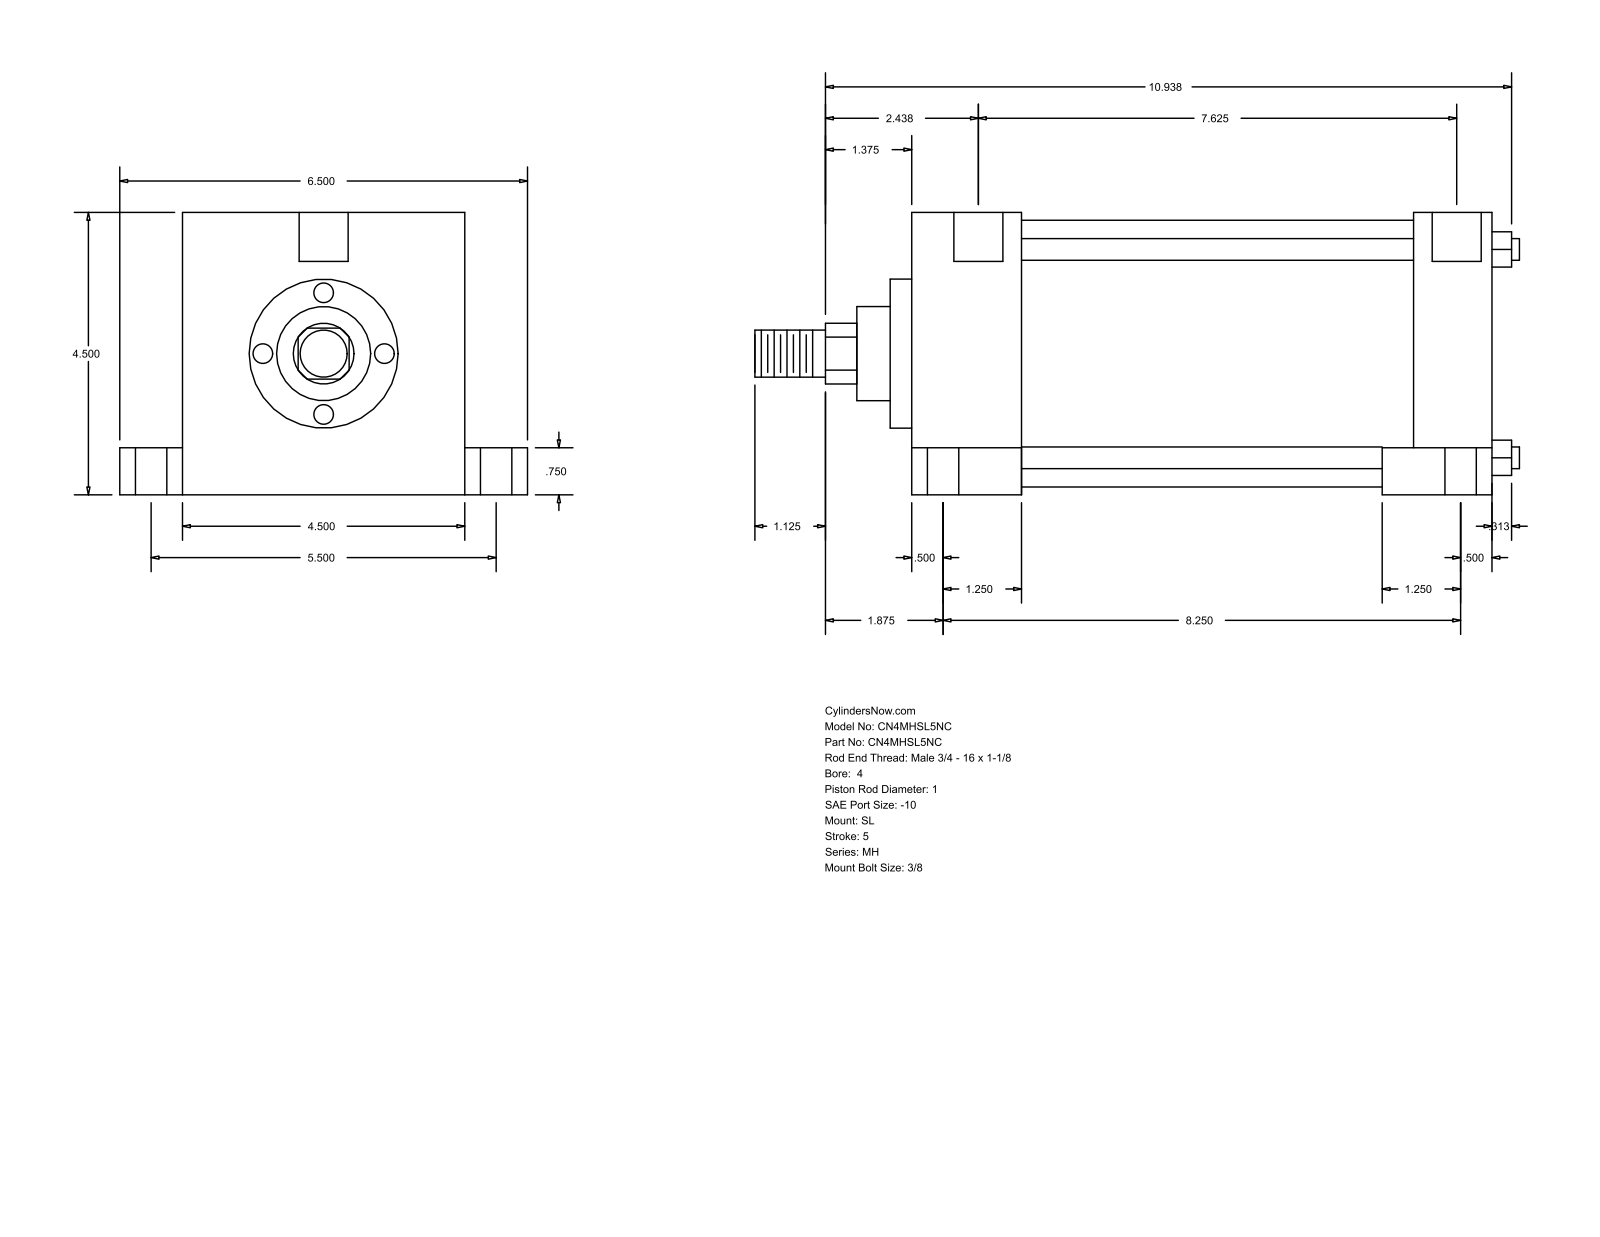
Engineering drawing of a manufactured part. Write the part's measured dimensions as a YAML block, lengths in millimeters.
part_name: "MH_SL__0400_1"
step_written_by: "GSSL Pune (CONFIG_CONTROL_DESIGN)"
units: millimeters
bodies: {solids: 0, faces: 110, planar: 77, cylindrical: 33, other: 0}
overall_size: [309.56, 165.1, 114.3]
round_holes:
  - {diameter: 8.73, count: 4}
  - {diameter: 12.7, count: 4}
  - {diameter: 19.05, count: 4}
  - {diameter: 19.84, count: 2}
round_bosses_or_shafts:
  - {diameter: 8.76, count: 4}
  - {diameter: 107.95, count: 1}
  - {diameter: 60.33, count: 1}
  - {diameter: 38.1, count: 1}
  - {diameter: 25.4, count: 1}
  - {diameter: 19.05, count: 1}
partial_cylinders:
  - {radius: 12.29, count: 1}
face_to_face_distances: [114.3, 234.96, 44.46, 190.5, 203.2, 158.74, 31.76, 25.4, 139.7, 19.05]
hole_center_spacings: [69.85, 69.87, 71, 71.3, 139.7, 196.85, 207.39, 208.88]
